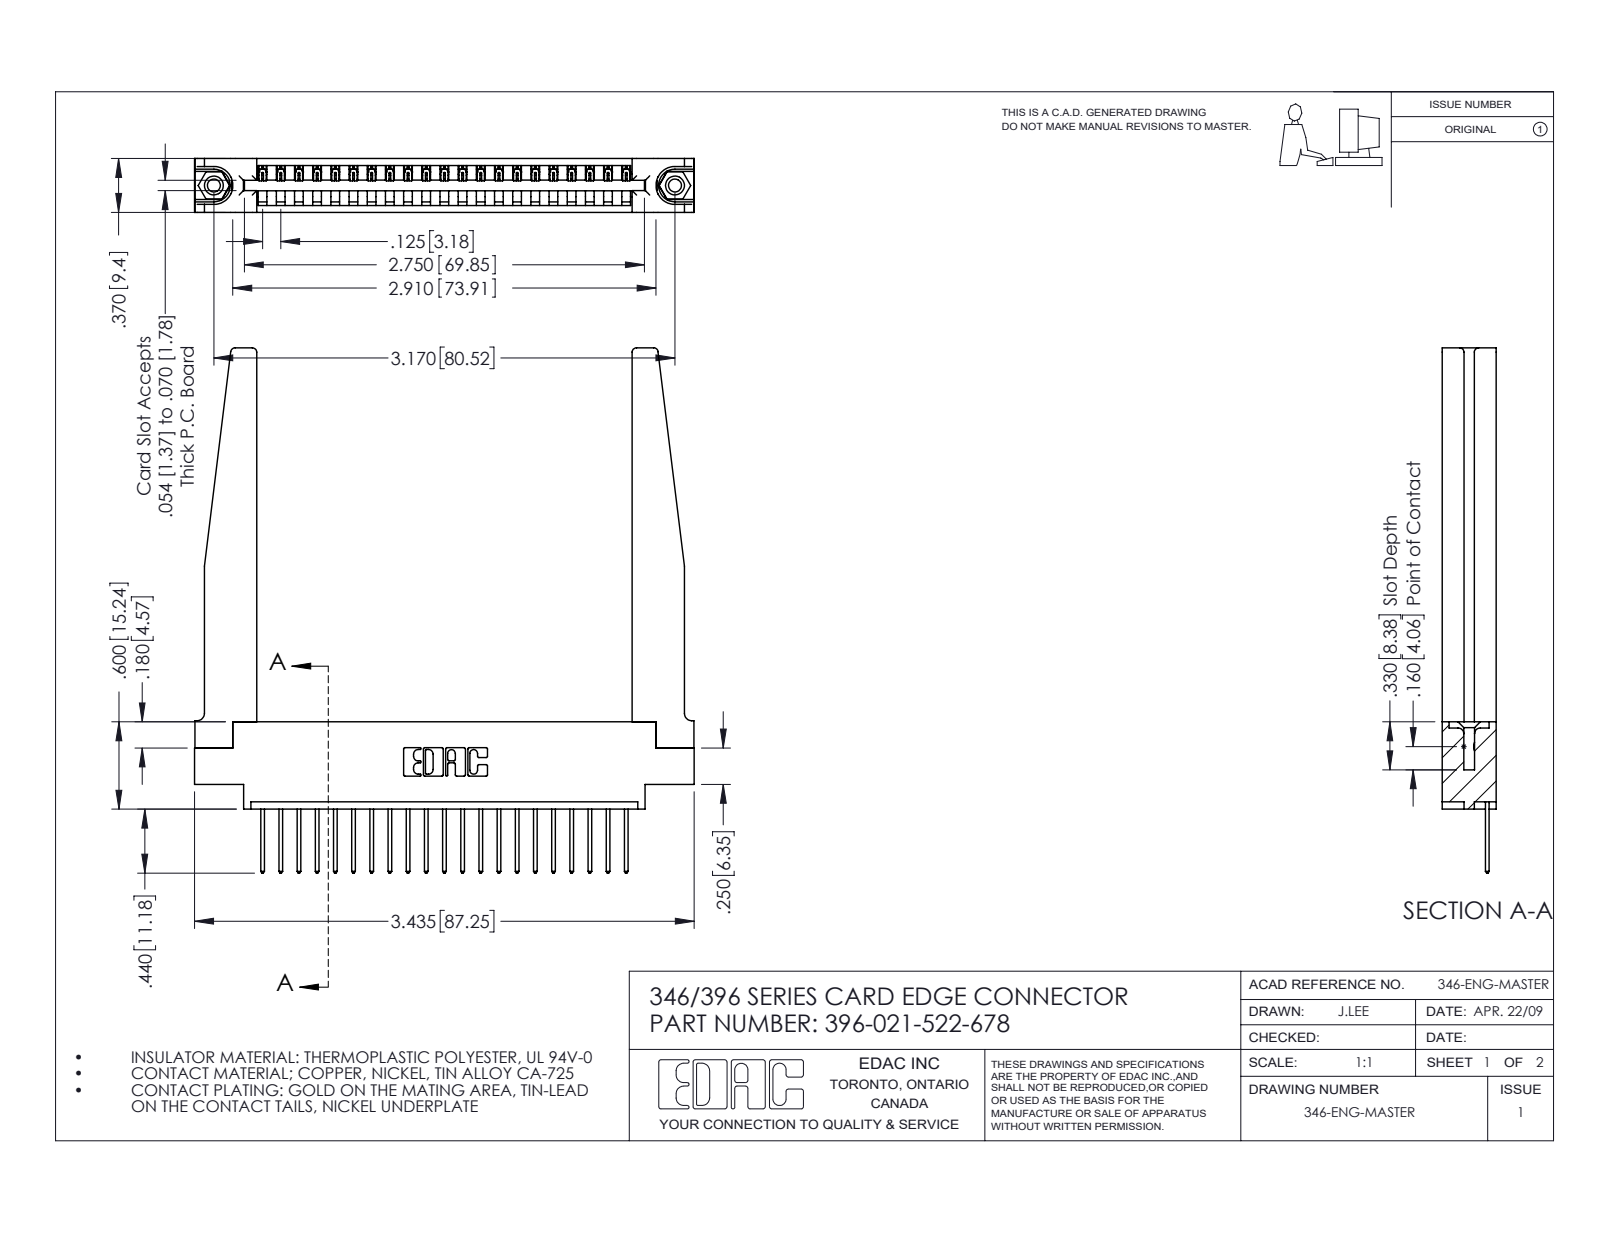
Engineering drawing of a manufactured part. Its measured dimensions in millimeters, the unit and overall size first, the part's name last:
Units: millimetres
Overall size (bounding box): 91.7 × 87.2 × 9.4
Round holes (diameter × count): ⌀2.3 ×2, ⌀3.2 ×2, ⌀4 ×2, ⌀1.6 ×1
Round bosses / shafts (diameter × count): ⌀3.9 ×2
Partial cylindrical surfaces — rounded edges, fillets, slot ends (radius × count): R0.2 ×42, R0.3 ×42, R0.3 ×22, R0.8 ×8, R0.2 ×6, R0.8 ×6, R0.7 ×3, R0.8 ×2
Main face-to-face distances: 9.4, 1.8, 1.2, 8.2, 3.8, 3.8, 6.4, 7.6, 0.6, 5.6
Hole centre spacings: 6.2, 75.3, 80.5
Volume: 15 000 mm³ · Surface area: 16 620 mm²
Bodies: 26 solids, 1578 faces (1062 planar, 464 cylindrical, 52 other)
Part name (STEP PRODUCT): 396-021-522-678; 346-220-078_345-220-078; 345-292-001_345-293-122; 345-250-001_345-250-001-102 (+1 more)
STEP written by: SolidWorks 2016 (CONFIG_CONTROL_DESIGN)
